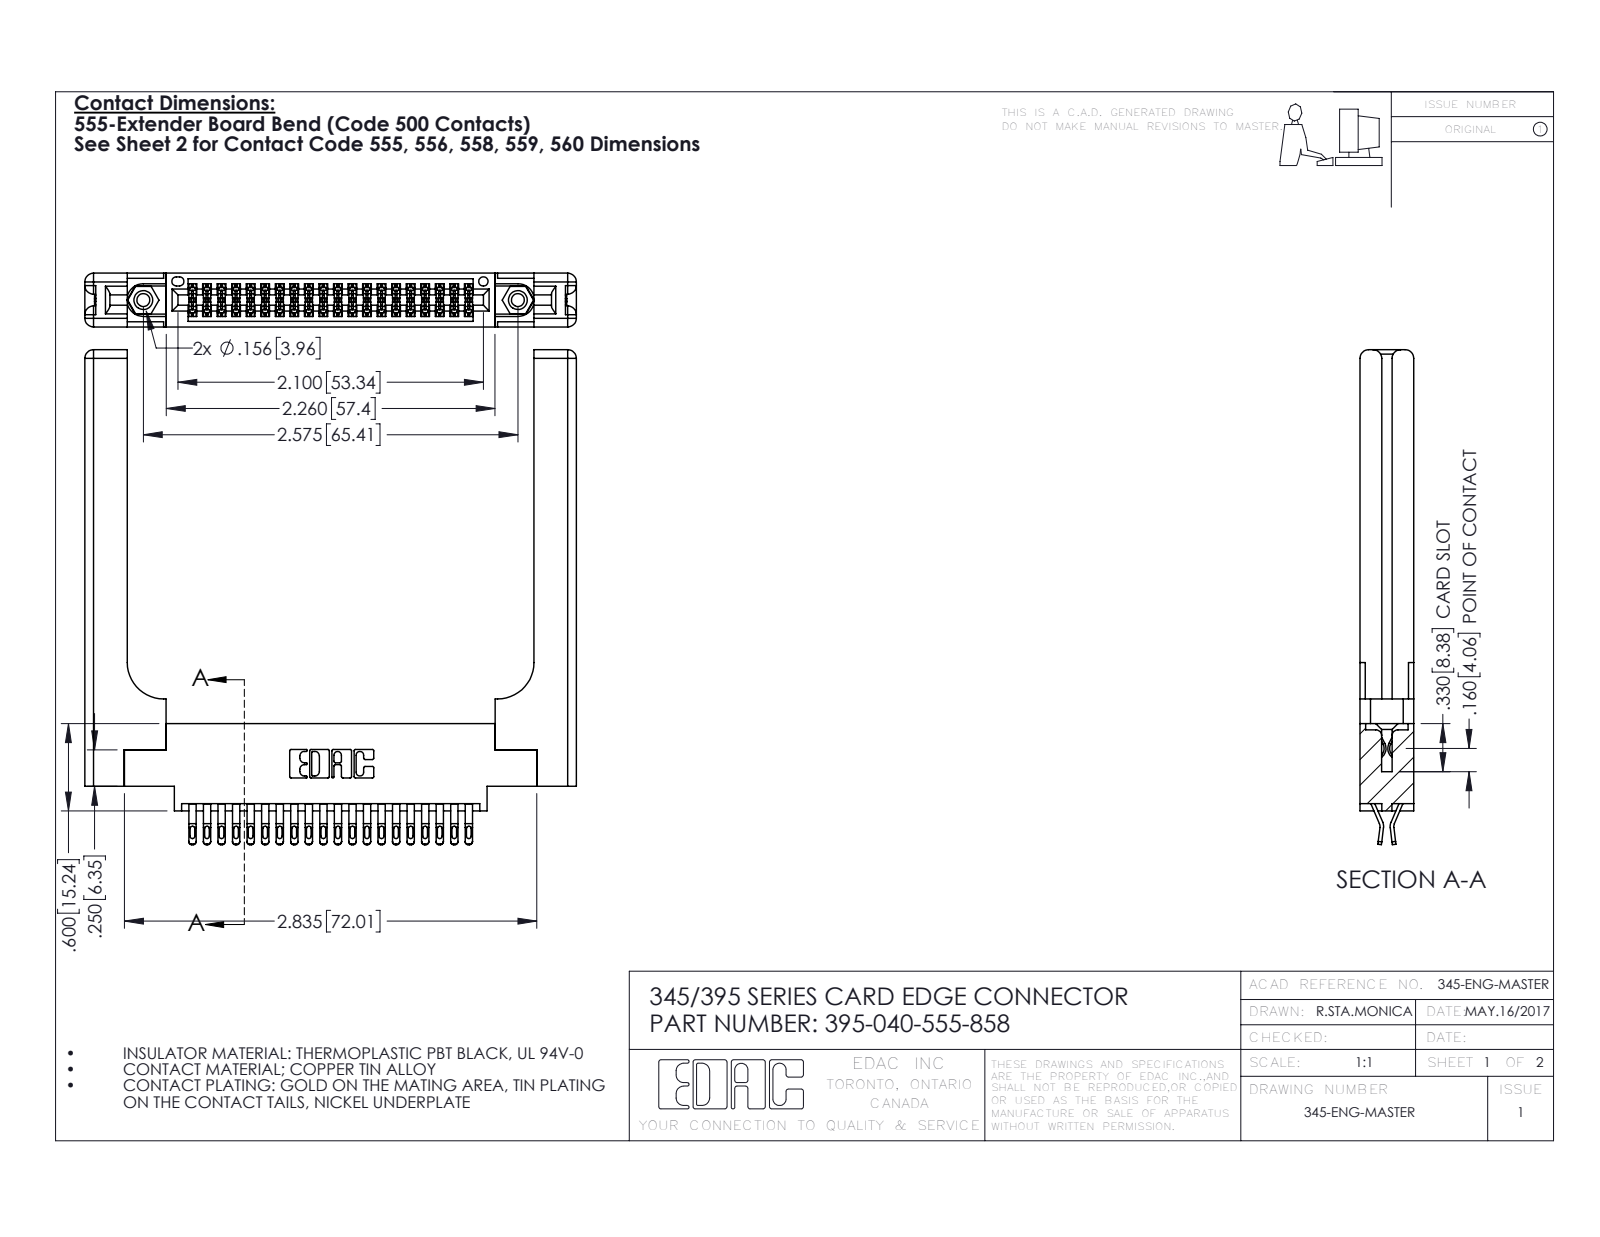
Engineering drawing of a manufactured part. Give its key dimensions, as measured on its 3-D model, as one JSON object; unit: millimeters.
{"part_name": "345 Part_0.170 Offset - 0.156 Dia-TH; 345-220-058_345-220-058; 345-250-001_345-250-001-102; 345-292-001_555 Tail (+1 more)", "step_written_by": "SolidWorks 2016 (CONFIG_CONTROL_DESIGN)", "units": "millimeters", "bodies": {"solids": 45, "faces": 2626, "planar": 1472, "cylindrical": 1094, "other": 60}, "overall_size": [86.4, 85.8, 9.4], "volume_mm3": 16620, "surface_area_mm2": 17210, "round_holes": [[2.3, 2], [3.2, 2], [4, 2], [1.6, 1]], "round_bosses_or_shafts": [[3.9, 2]], "partial_cylinders_radius": [[0.4, 100], [0.5, 80], [0.2, 60], [0.3, 22], [1.5, 16], [0.2, 6], [0.8, 6], [0.7, 3]], "face_to_face_distances": [9.4, 1.8, 7.6, 3.8, 3.8, 2, 0.6, 5.6, 5.7, 3.1], "hole_center_spacings": [6.9, 59.5, 65.4]}
